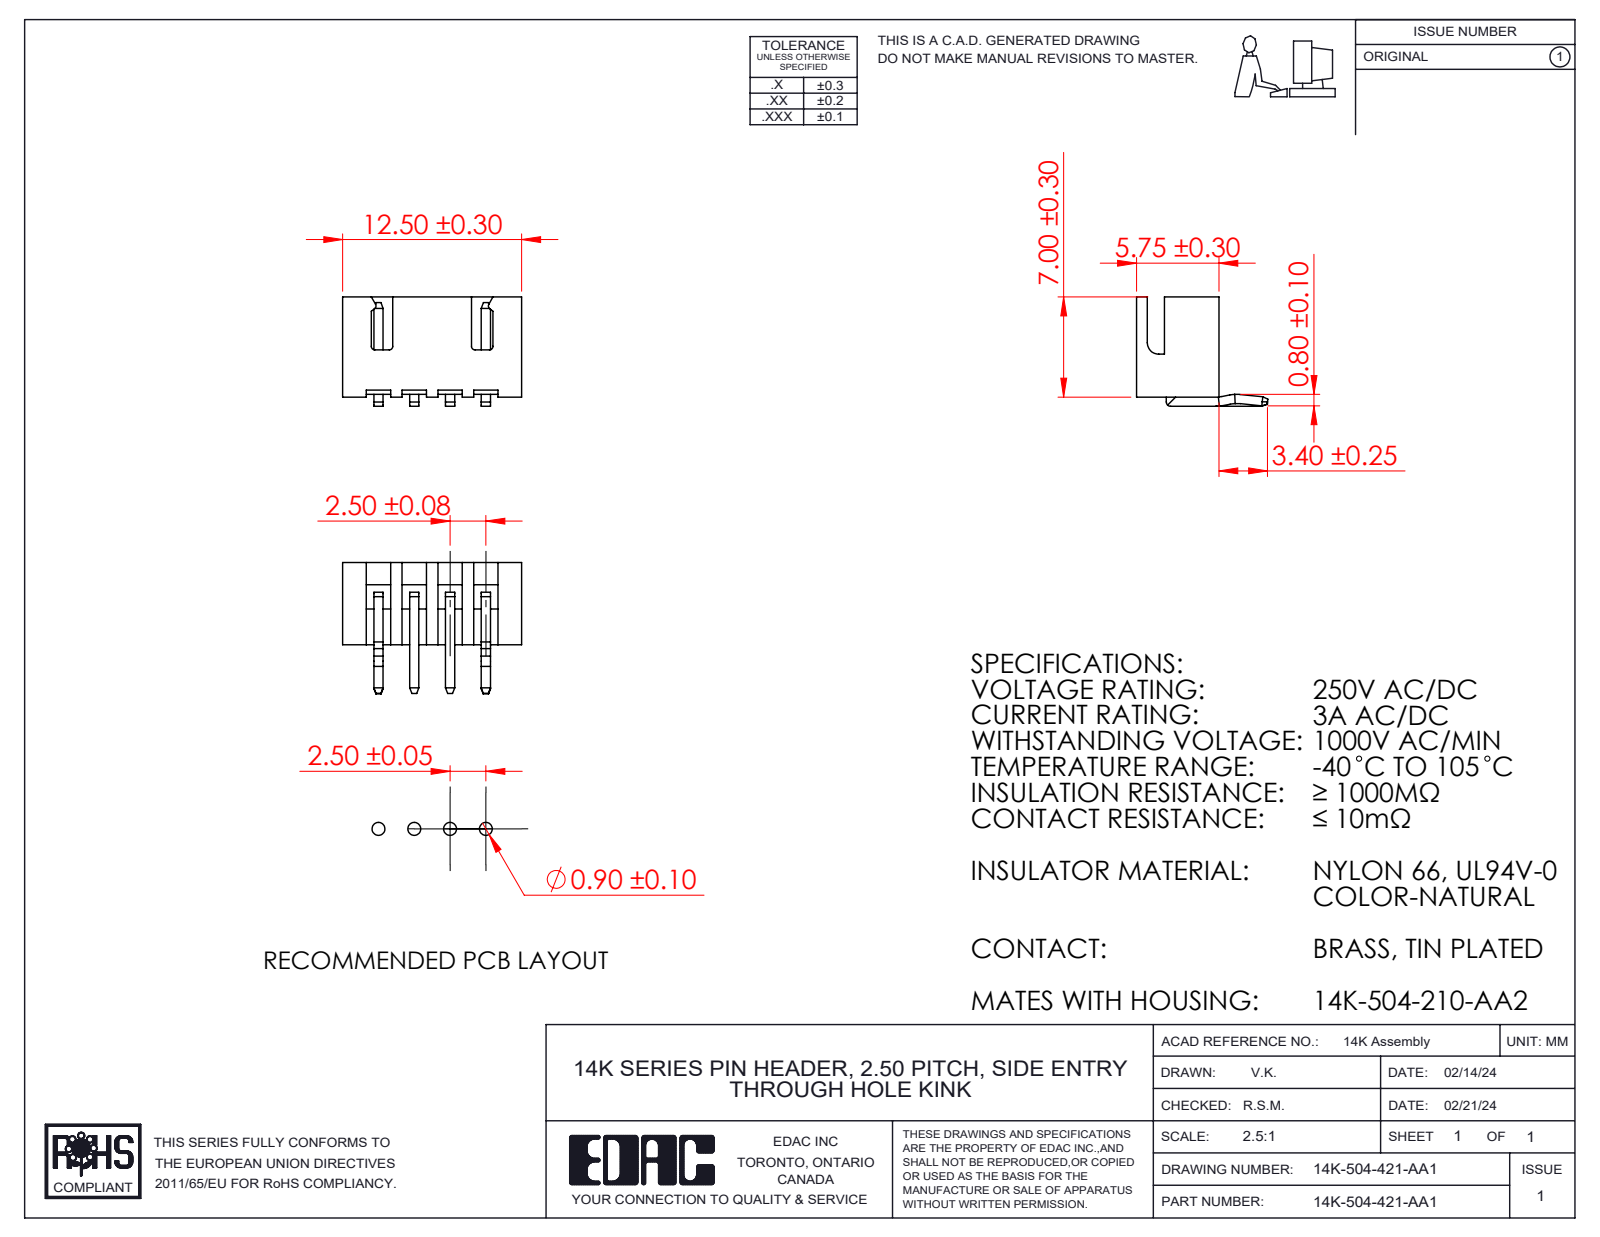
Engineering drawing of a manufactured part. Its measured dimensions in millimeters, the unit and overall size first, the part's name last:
Units: millimetres
Overall size (bounding box): 12.5 × 9.17 × 7.64
Partial cylindrical surfaces — rounded edges, fillets, slot ends (radius × count): R0.25 ×6, R0.3 ×4, R2.5 ×4, R0.8 ×1
Main face-to-face distances: 5, 0.76, 5.76, 0.64, 2.5, 4.24, 12.5, 0.75, 11.75, 1.7
Volume: 249 mm³ · Surface area: 705 mm²
Bodies: 5 solids, 196 faces (167 planar, 29 cylindrical, 0 other)
Part name (STEP PRODUCT): 14K Series Pin Header Insulator_504; 14K Series Pin_21; 14K-504-421-AA1; 14K Series Pin_16
STEP written by: SolidWorks 2023 (CONFIG_CONTROL_DESIGN)
